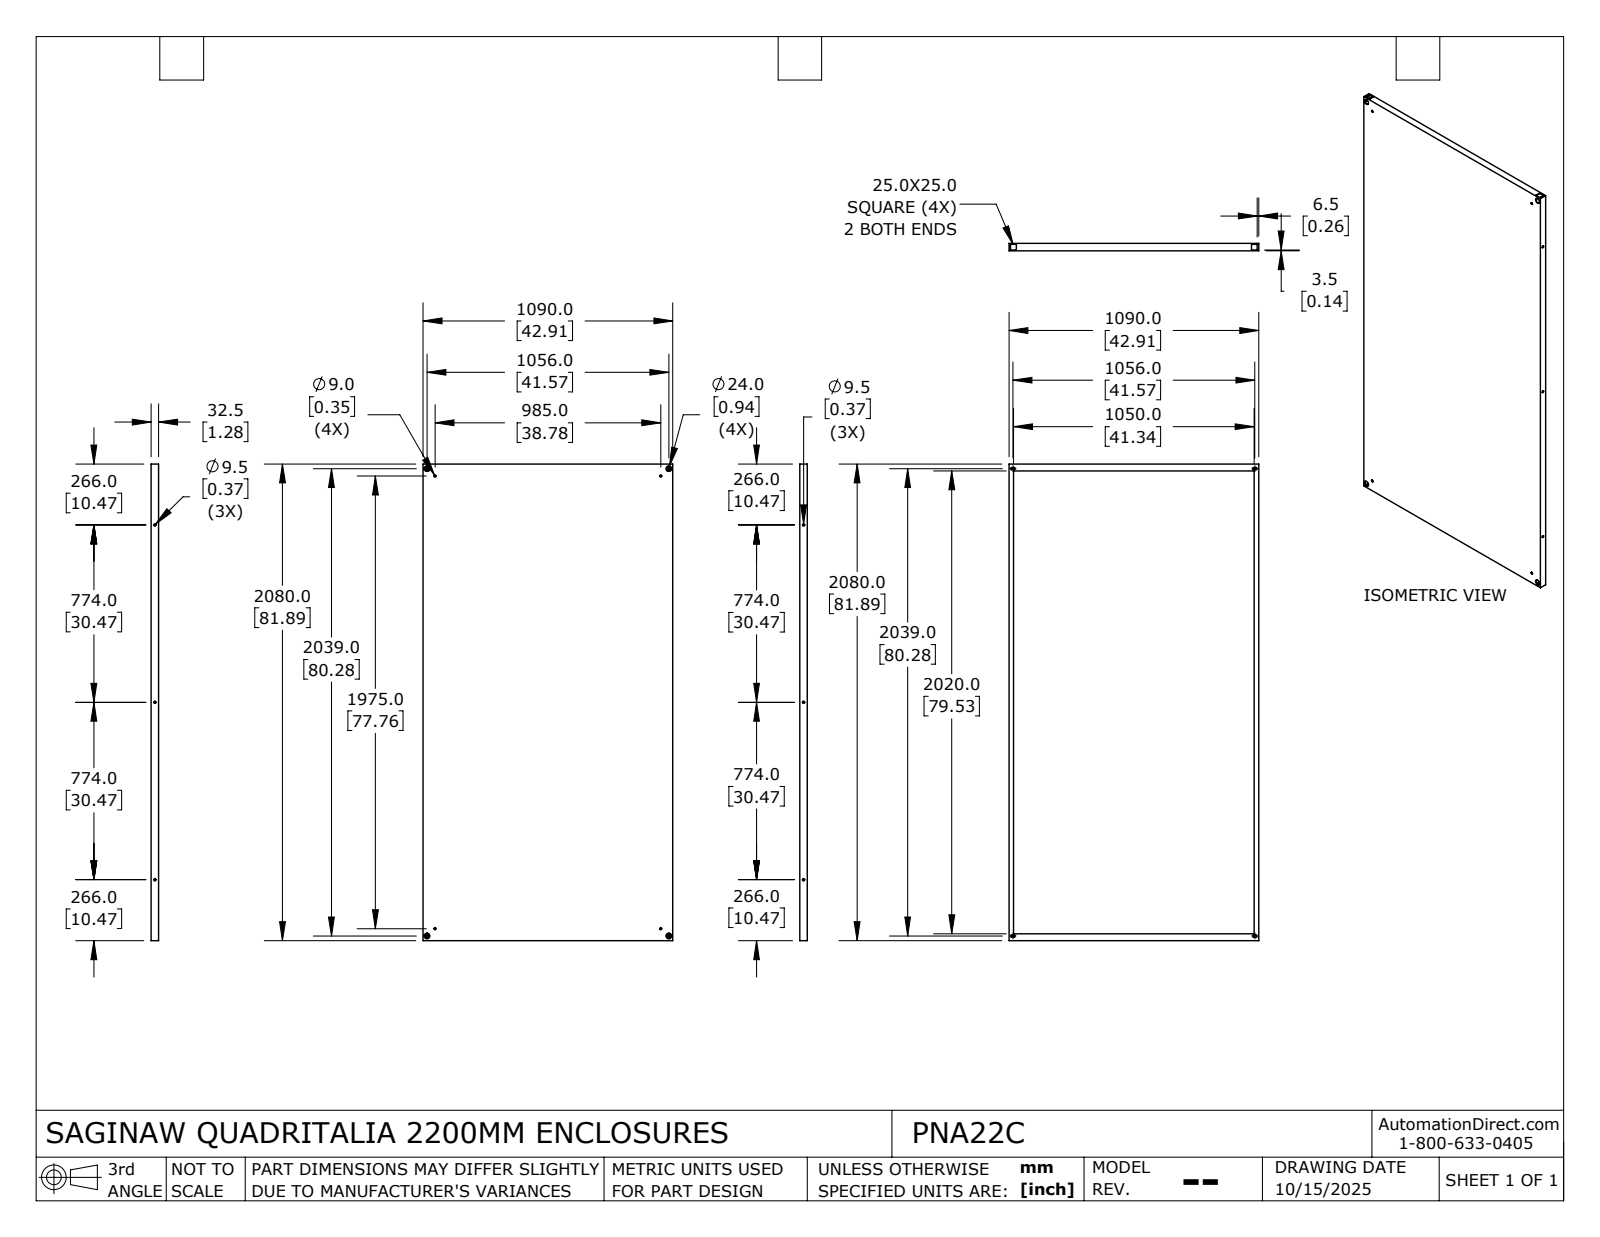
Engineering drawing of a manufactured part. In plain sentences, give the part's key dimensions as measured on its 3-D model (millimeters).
The part is named "PNA22C_Default". Its 3-D file was written by "SolidWorks 2024 (CONFIG_CONTROL_DESIGN)". It is 1 solid with 70 faces: 48 planar, 22 cylindrical and 0 other. Overall it measures 2080 by 1090 by 32.5 millimeters. Its volume is 6 454 000 cubic millimeters and its surface area 5 182 000 square millimeters. Round holes: 4 of diameter 9, 4 of diameter 24, 3 of diameter 9.5. Partial cylindrical surfaces (rounded edges, fillets, slot ends): 8 of radius 5. The main face-to-face distances are 2.5, 30, 32.5, 27.5, 1087.5, 1090, 2077.5, 1085, 2080, 2075. The hole center spacings are 47.79, 1021, 2007.31, 2251.55, 774, 985, 1056, 1975.
